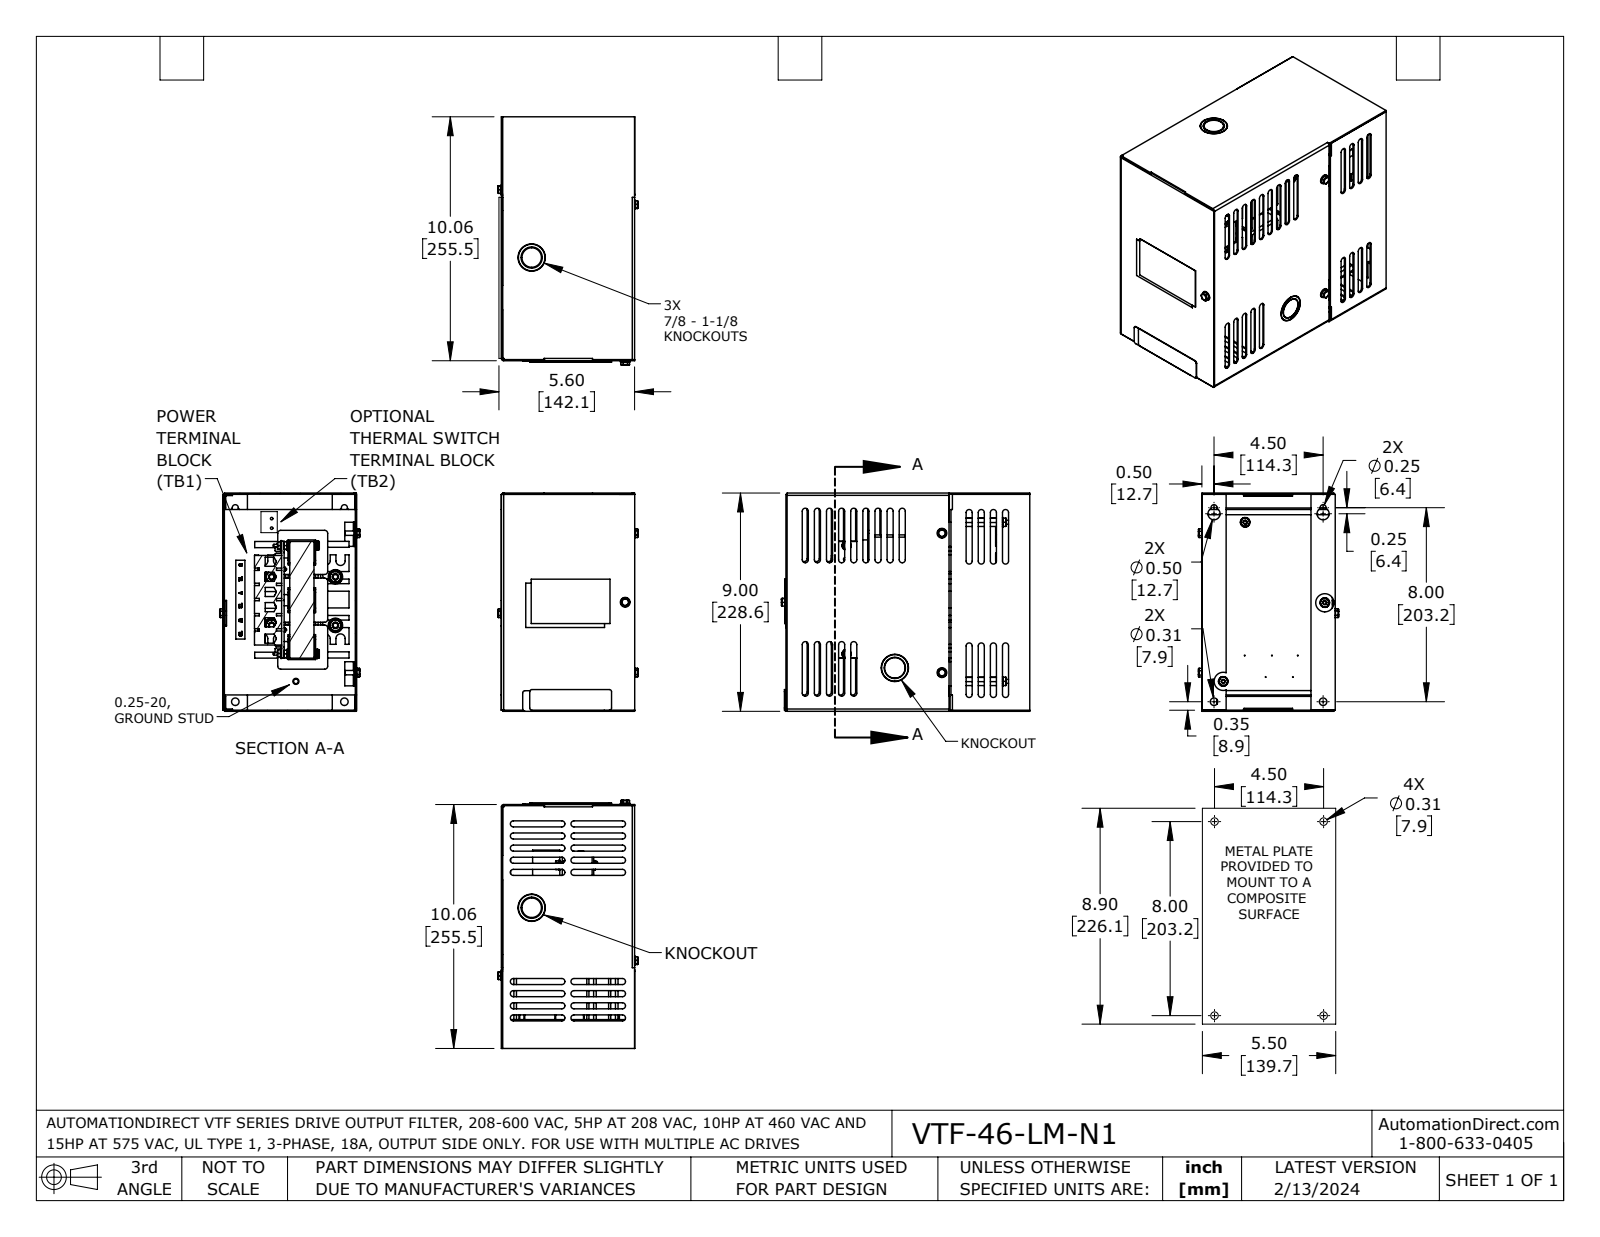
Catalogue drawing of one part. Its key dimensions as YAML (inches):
part_name: "VTF-46-LM-N1"
step_written_by: "SolidWorks 2021 (AUTOMOTIVE_DESIGN)"
units: inches
bodies: {solids: 42, faces: 2962, planar: 1795, cylindrical: 732, other: 435}
overall_size: [10.244, 9, 5.787]
volume: 51.11
surface_area: 1219
round_holes:
  - {diameter: 0.276, count: 16}
  - {diameter: 0.104, count: 7}
  - {diameter: 0.31, count: 7}
  - {diameter: 0.03, count: 6}
  - {diameter: 0.14, count: 6}
  - {diameter: 0.164, count: 5}
  - {diameter: 0.186, count: 5}
  - {diameter: 0.16, count: 4}
  - {diameter: 0.196, count: 4}
  - {diameter: 0.25, count: 4}
  - {diameter: 0.165, count: 3}
  - {diameter: 0.19, count: 3}
round_bosses_or_shafts:
  - {diameter: 0.25, count: 5}
  - {diameter: 0.38, count: 4}
  - {diameter: 0.181, count: 4}
  - {diameter: 0.19, count: 2}
  - {diameter: 0.164, count: 2}
  - {diameter: 0.15, count: 2}
  - {diameter: 1.125, count: 1}
partial_cylinders:
  - {radius: 0.125, count: 130}
  - {radius: 0.03, count: 68}
  - {radius: 0.05, count: 20}
  - {radius: 0.155, count: 17}
  - {radius: 0.09, count: 14}
  - {radius: 0.019, count: 12}
  - {radius: 0.039, count: 12}
  - {radius: 0.049, count: 12}
face_to_face_distances: [0.048, 0.059, 8.952, 0.047, 2, 5.448, 5.495, 5.4, 5.447, 0.05]
hole_center_spacings: [0.465, 3.555, 1.24, 1.25, 1.328, 1.939, 0.378, 0.381]
